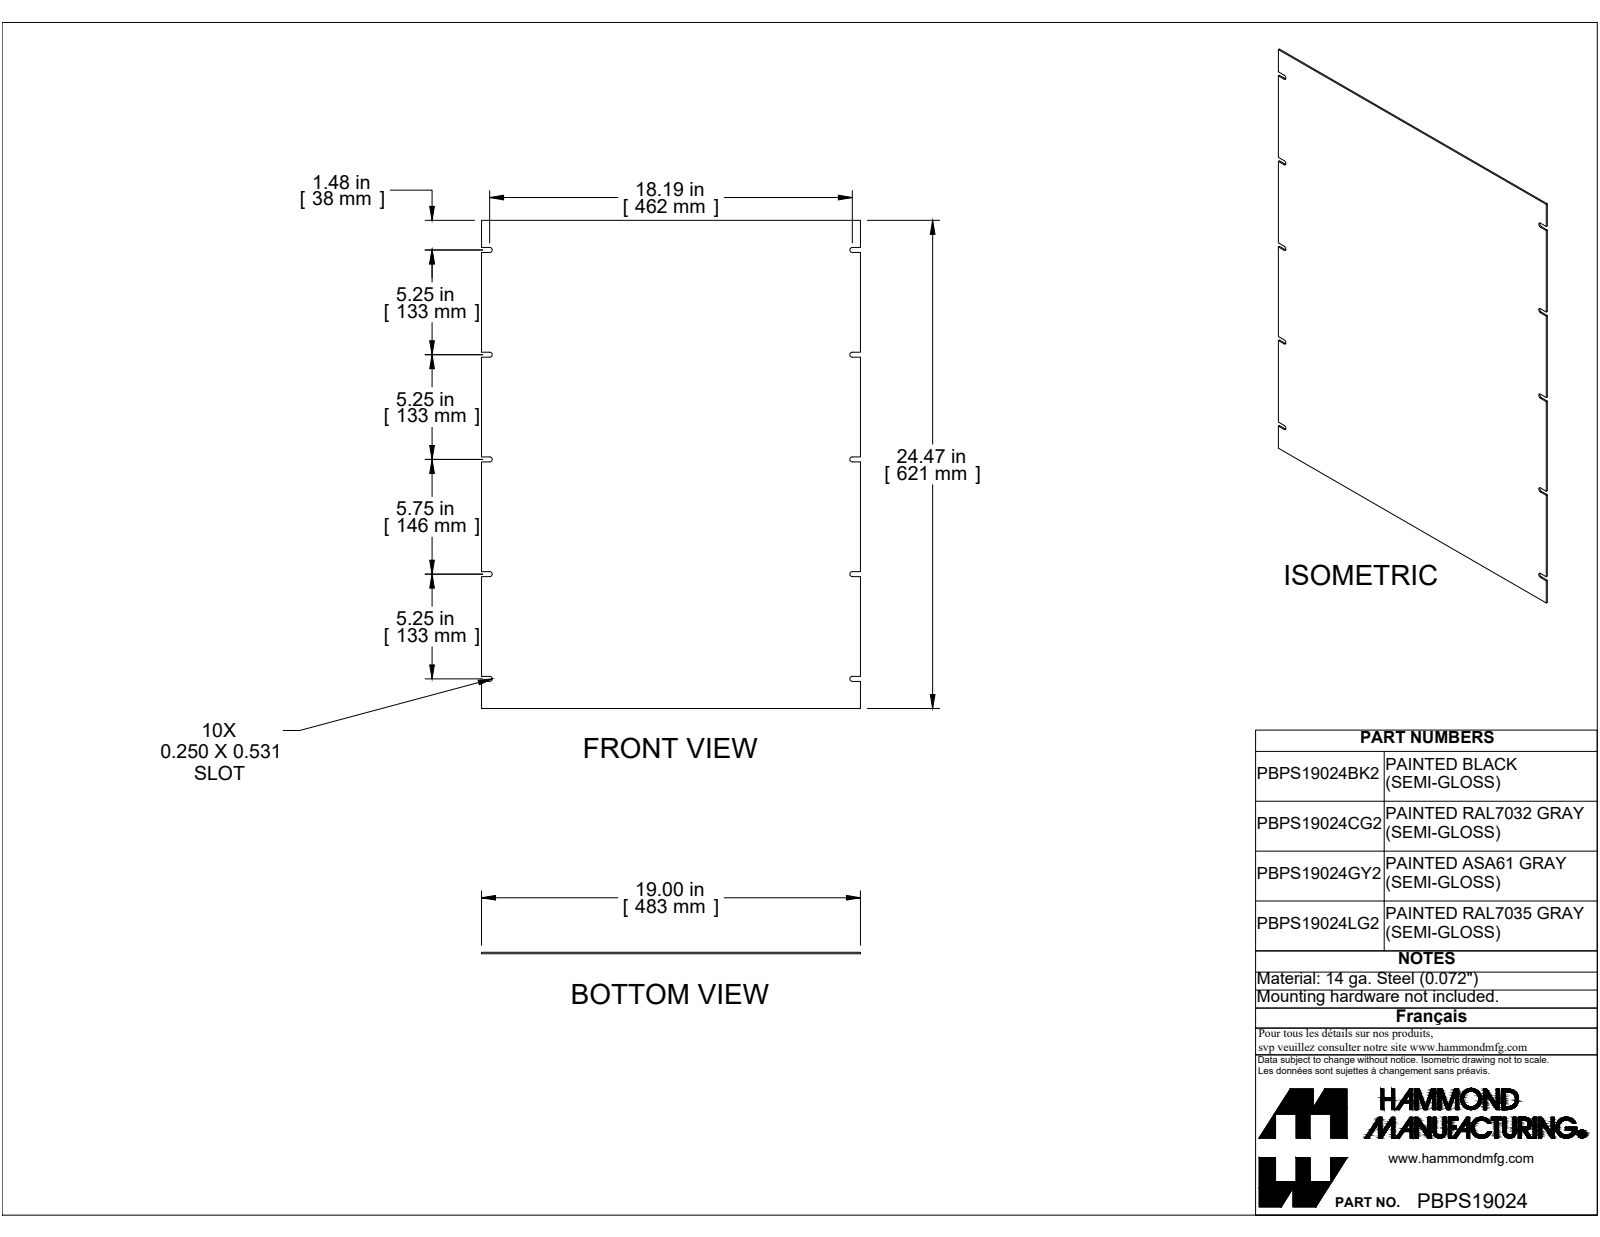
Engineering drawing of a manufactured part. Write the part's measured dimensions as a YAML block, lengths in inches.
part_name: "PBPS19024GY2"
step_written_by: "SolidWorks 2019 (CONFIG_CONTROL_DESIGN)"
units: inches
bodies: {solids: 1, faces: 46, planar: 36, cylindrical: 10, other: 0}
overall_size: [24.468, 19, 0.072]
volume: 33.38
surface_area: 934.2
partial_cylinders:
  - {radius: 0.125, count: 10}
face_to_face_distances: [0.072, 19, 24.468, 5.25, 0.25, 16.25, 11, 5.5, 6.859, 17.609]
